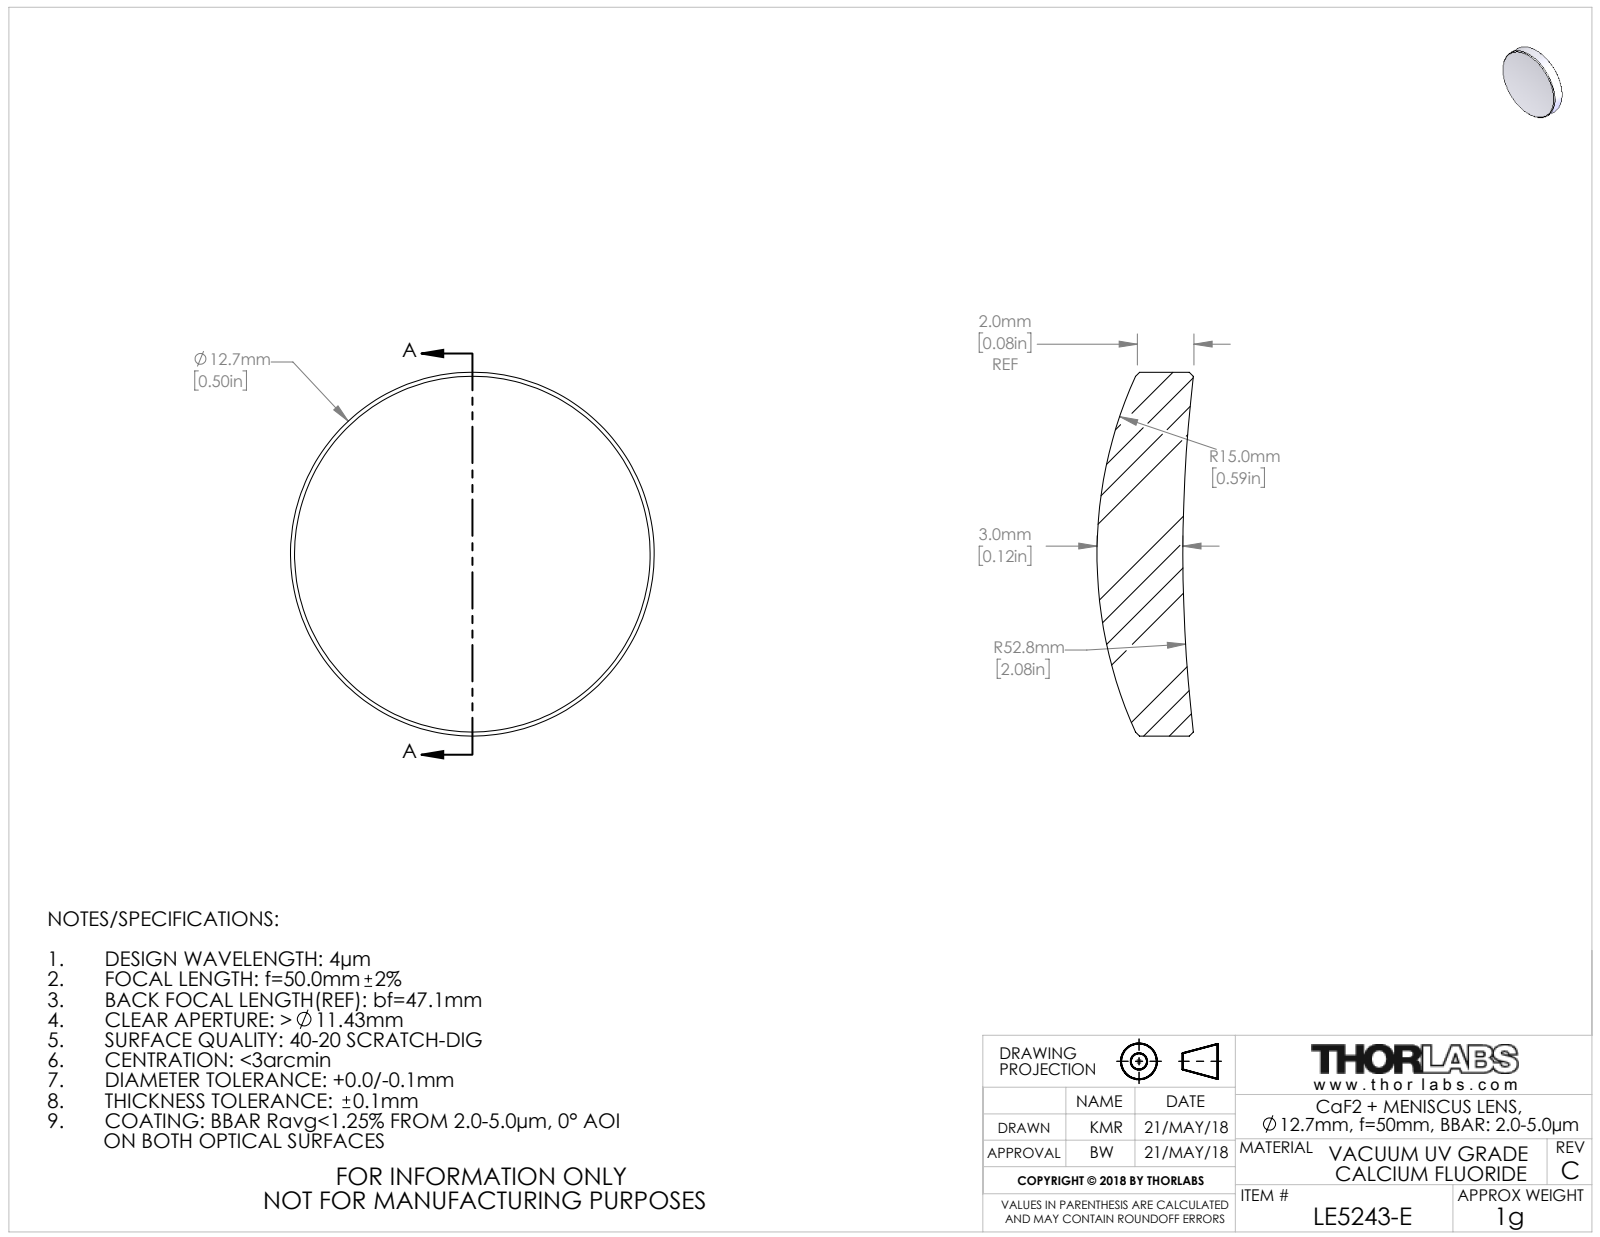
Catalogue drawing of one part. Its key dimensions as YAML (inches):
part_name: "20170-E0W"
step_written_by: "SolidWorks 2016 (CONFIG_CONTROL_DESIGN)"
units: inches
bodies: {solids: 1, faces: 10, planar: 0, cylindrical: 2, other: 8}
overall_size: [0.5, 0.5, 0.133]
volume: 0.019
surface_area: 0.517
round_bosses_or_shafts:
  - {diameter: 0.5, count: 1}
